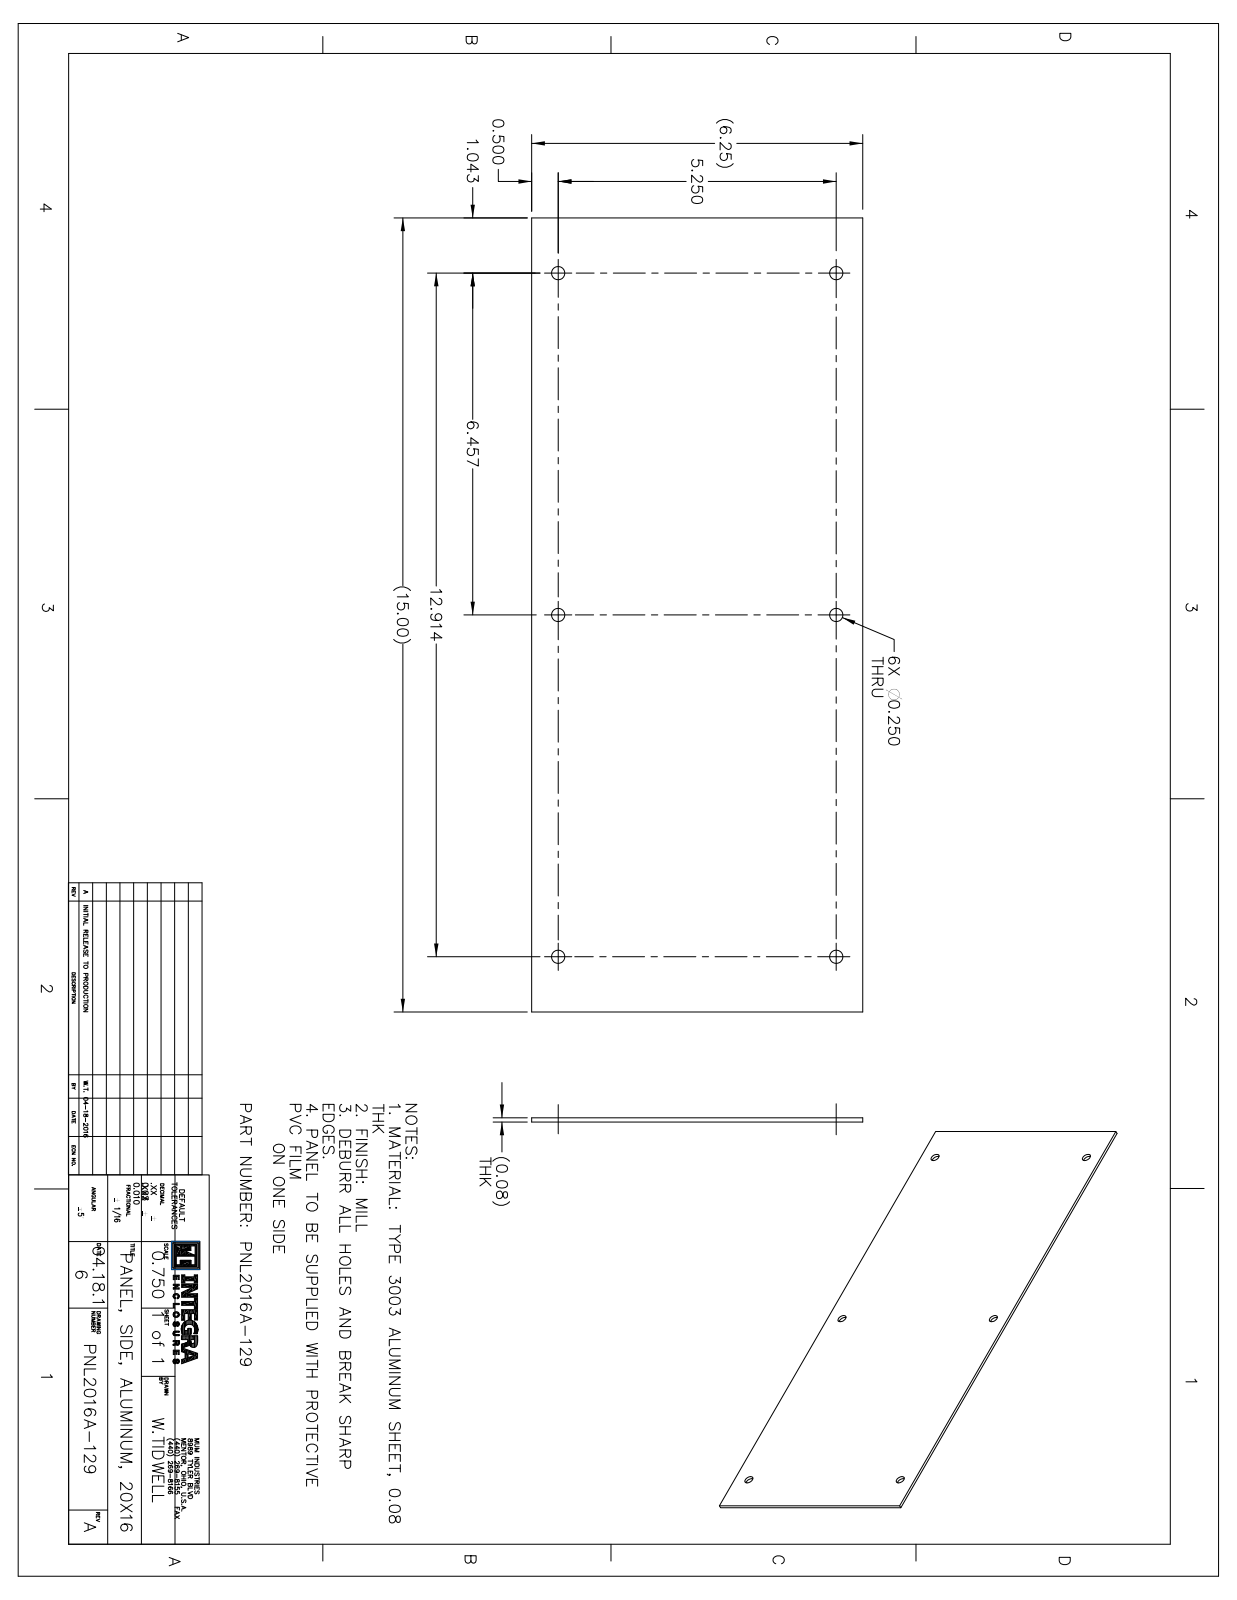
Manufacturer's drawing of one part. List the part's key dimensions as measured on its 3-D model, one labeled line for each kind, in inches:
Part name (STEP PRODUCT): ASP-2016-P10
STEP written by: SolidWorks 2018 (AUTOMOTIVE_DESIGN)
Units: inches
Bodies: 1 solid, 12 faces (6 planar, 6 cylindrical, 0 other)
Overall size (bounding box): 15 × 6.25 × 0.08
Volume: 7.476 in³ · Surface area: 190.7 in²
Round holes (diameter × count): ⌀0.25 ×6
Main face-to-face distances: 0.08, 6.25, 15
Hole centre spacings: 6.457, 8.322, 5.25, 12.914, 13.941
